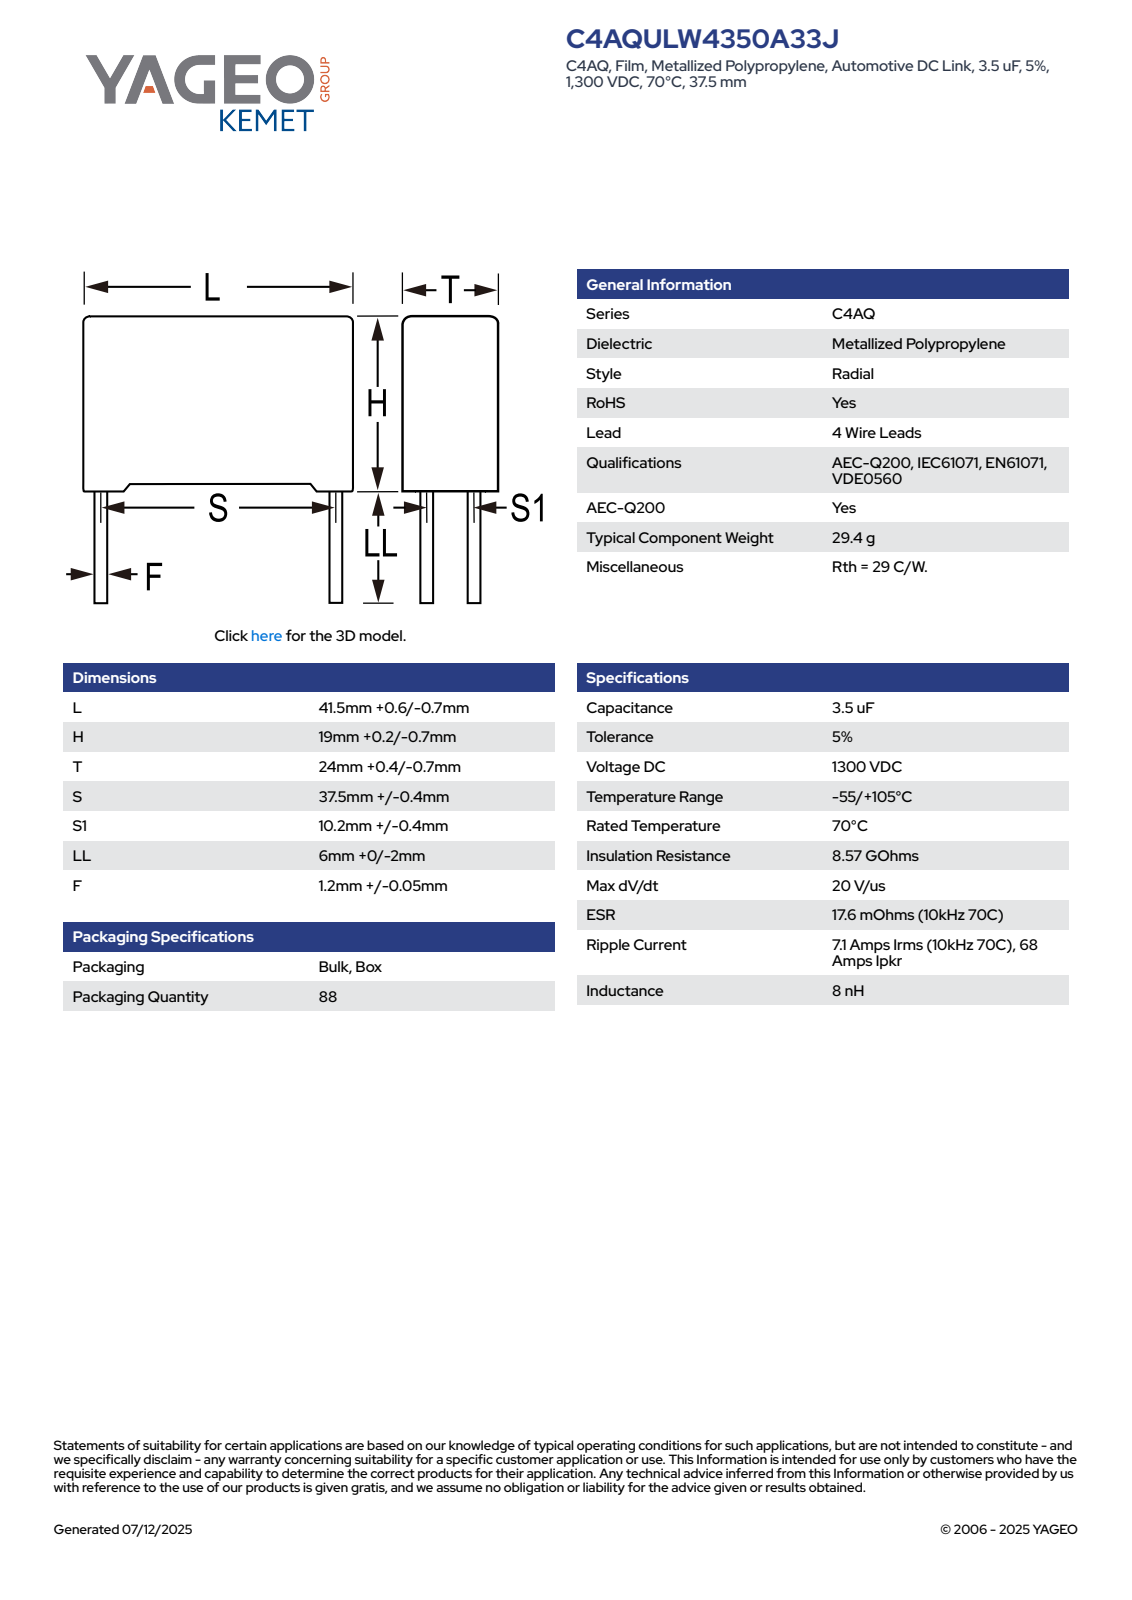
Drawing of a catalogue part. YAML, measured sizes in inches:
part_name: "CFP_RB4_41.5X19X24_L42.1H19.2T24.4S37.5S110.2LL6F1.25"
step_written_by: "SolidWorks 2014 (AUTOMOTIVE_DESIGN)"
units: inches
bodies: {solids: 4, faces: 87, planar: 79, cylindrical: 8, other: 0}
overall_size: [1.657, 0.992, 0.961]
volume: 1.174
surface_area: 7.49
round_bosses_or_shafts:
  - {diameter: 0.049, count: 4}
face_to_face_distances: [0.734, 0.961, 1.657, 0.022, 0.756, 0.961, 0.059, 1.598, 0.902, 1.539]
